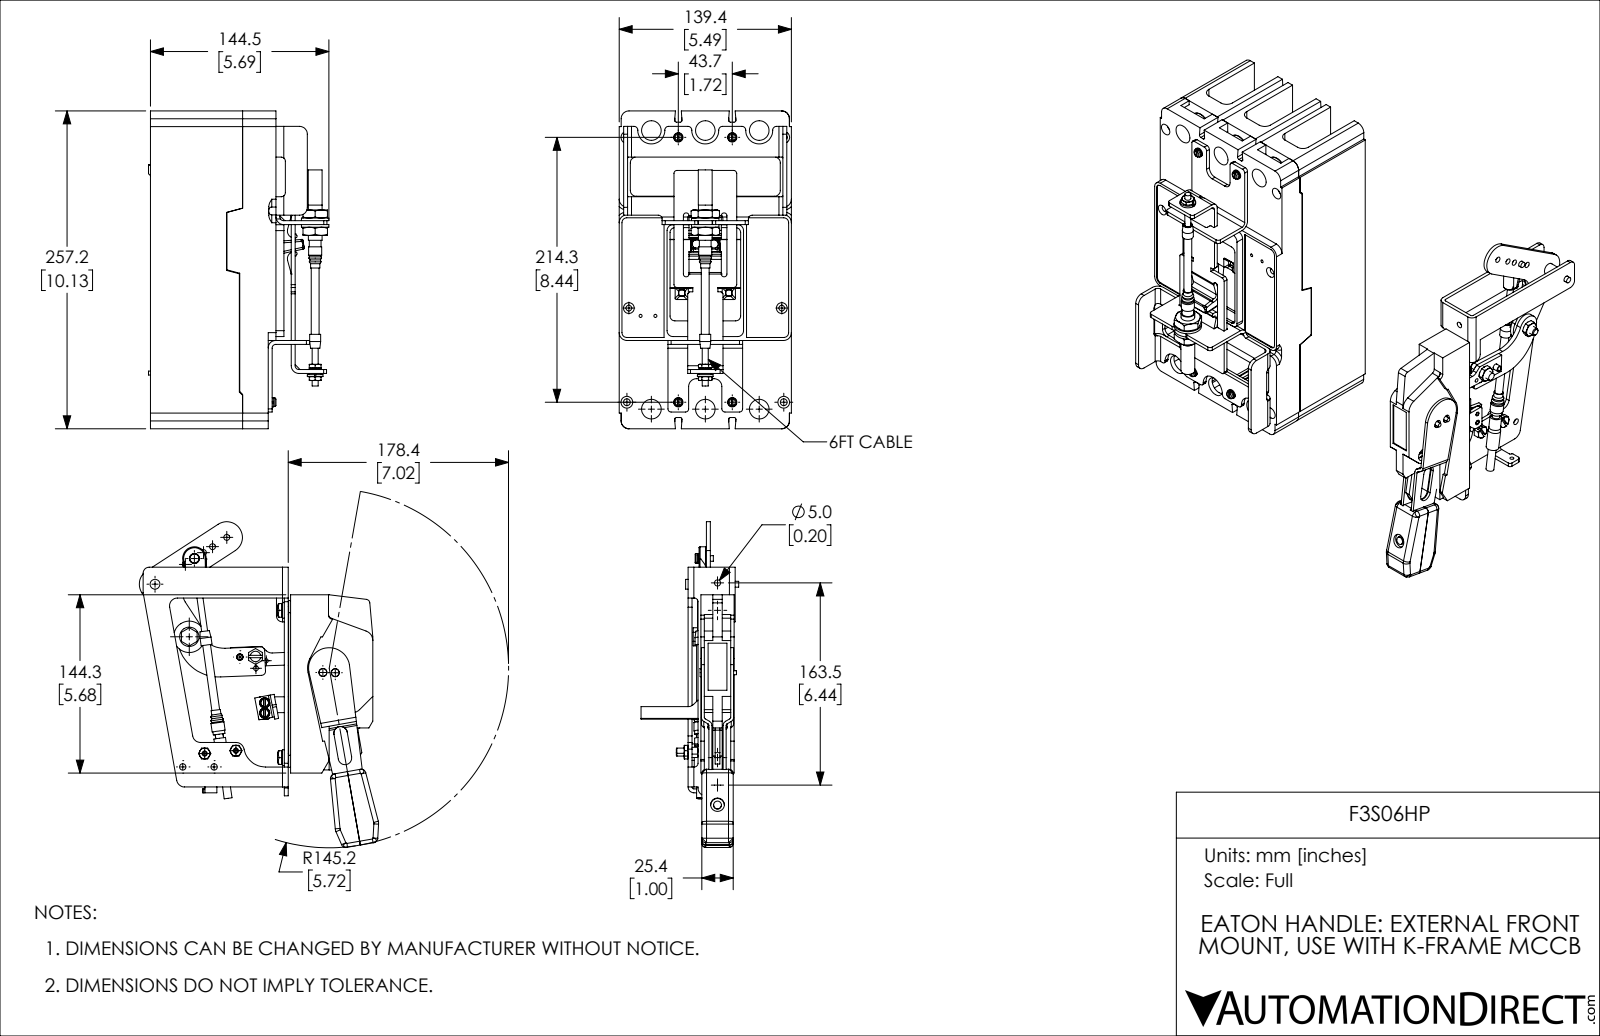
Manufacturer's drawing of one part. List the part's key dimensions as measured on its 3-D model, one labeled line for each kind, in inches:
Part name (STEP PRODUCT): F3S06HP_BREAKER; F3S06HP; F3S06HP_HANDLE
STEP written by: SolidWorks 2019 (CONFIG_CONTROL_DESIGN)
Units: inches
Bodies: 81 solids, 2972 faces (1428 planar, 1143 cylindrical, 401 other)
Overall size (bounding box): 14.165 × 10.378 × 7.627
Volume: 182.3 in³ · Surface area: 888.8 in²
Round holes (diameter × count): ⌀0.219 ×8, ⌀0.203 ×6, ⌀0.228 ×6, ⌀0.625 ×6, ⌀0.188 ×5, ⌀0.196 ×5, ⌀0.281 ×5, ⌀0.375 ×5, ⌀0.438 ×5, ⌀0.168 ×4, ⌀0.25 ×4, ⌀0.5 ×4
Round bosses / shafts (diameter × count): ⌀0.25 ×9, ⌀0.338 ×6, ⌀0.375 ×5, ⌀0.5 ×4, ⌀0.297 ×4, ⌀0.27 ×4, ⌀0.138 ×4, ⌀0.394 ×3
Partial cylindrical surfaces — rounded edges, fillets, slot ends (radius × count): R0.062 ×109, R0.125 ×53, R0.25 ×50, R0.032 ×22, R0.156 ×18, R0.1 ×16, R0.188 ×16, R0.031 ×15
Main face-to-face distances: 0.125, 5.49, 0.249, 2.906, 1.062, 3.719, 0.813, 0.032, 4, 0.156
Hole centre spacings: 1.719, 8.17, 7.907, 8.7, 9.04, 0.531, 1.141, 1.141
